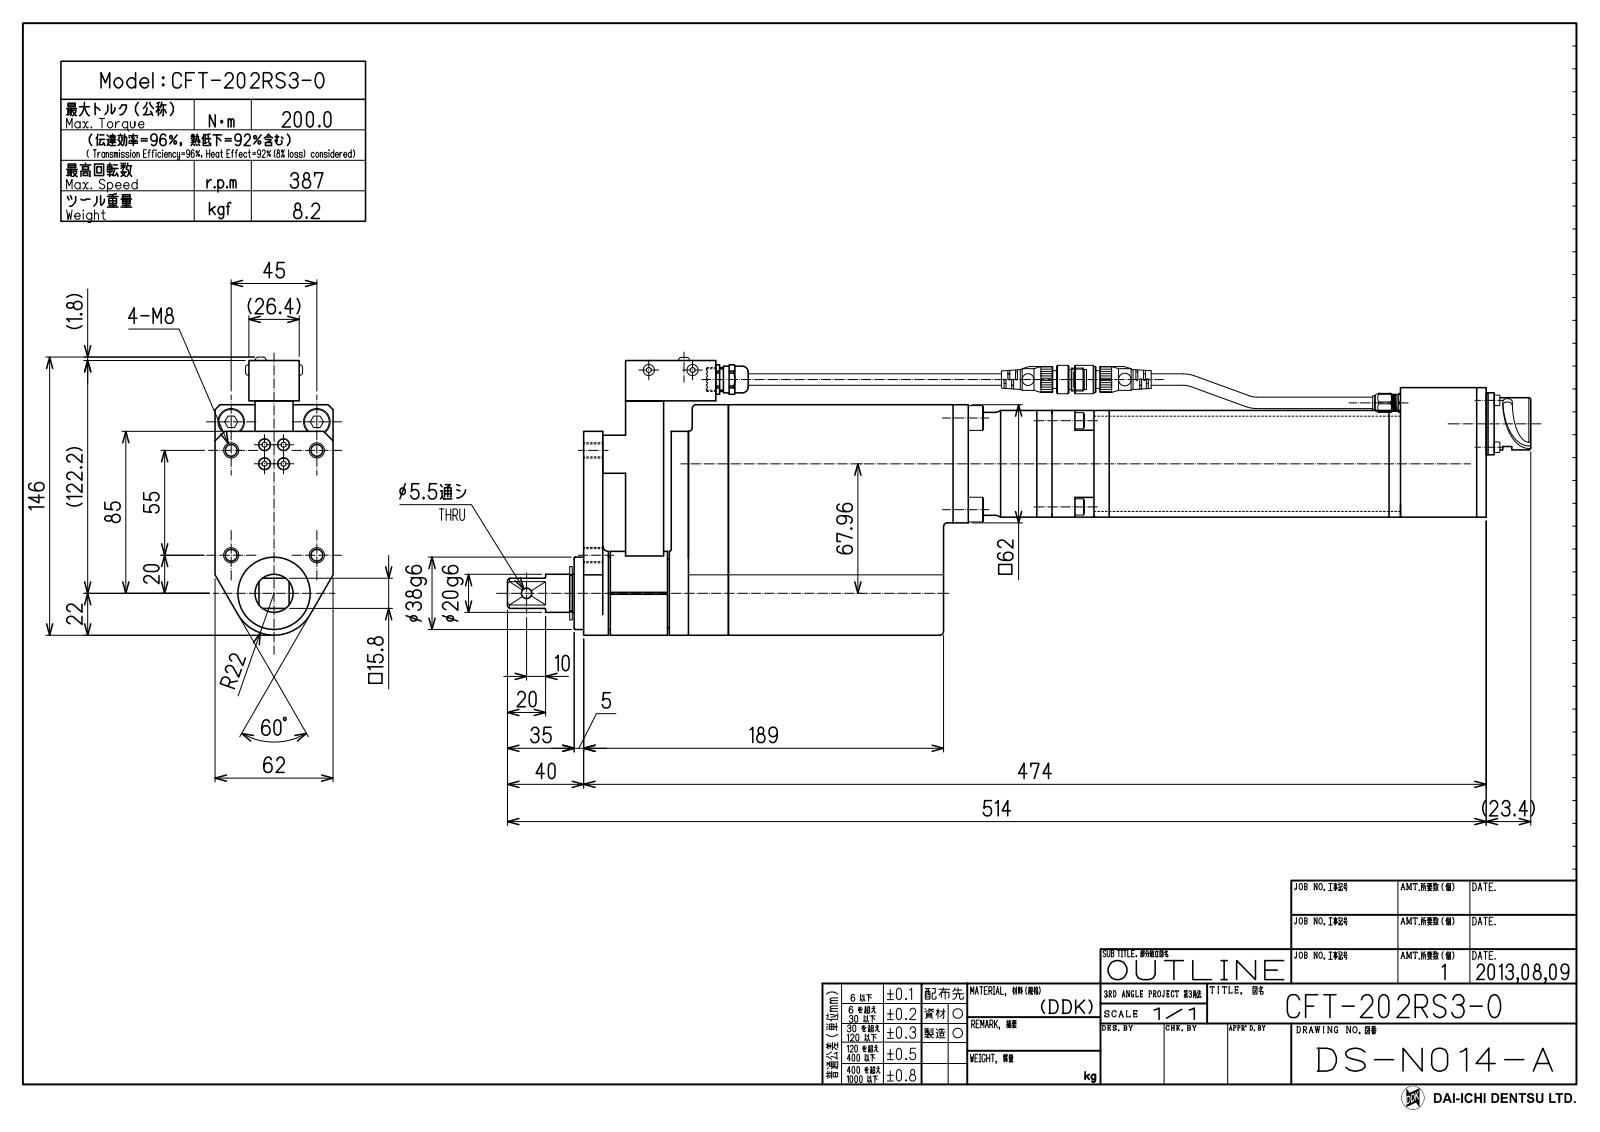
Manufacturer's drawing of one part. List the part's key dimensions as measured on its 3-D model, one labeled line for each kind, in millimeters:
Part name (STEP PRODUCT): CFT-202RS3-O
STEP written by: SolidWorks 2013 (CONFIG_CONTROL_DESIGN)
Units: millimetres
Bodies: 22 solids, 401 faces (202 planar, 136 cylindrical, 63 other)
Overall size (bounding box): 536.4 × 145.85 × 62
Volume: 1 840 000 mm³ · Surface area: 229 838 mm²
Round holes (diameter × count): ⌀6.8 ×4, ⌀5.5 ×1, ⌀20.8 ×1
Round bosses / shafts (diameter × count): ⌀13 ×4, ⌀7 ×4, ⌀5.6 ×2, ⌀56 ×1, ⌀54 ×1, ⌀44 ×1, ⌀38 ×1, ⌀28 ×1
Partial cylindrical surfaces — rounded edges, fillets, slot ends (radius × count): R2 ×12, R1 ×7, R3 ×4, R9 ×2, R12 ×2, R24.5 ×1
Main face-to-face distances: 21, 62, 30, 8, 183, 191, 192, 46, 423, 200
Hole centre spacings: 26.47, 45, 55, 71.06, 72.52
